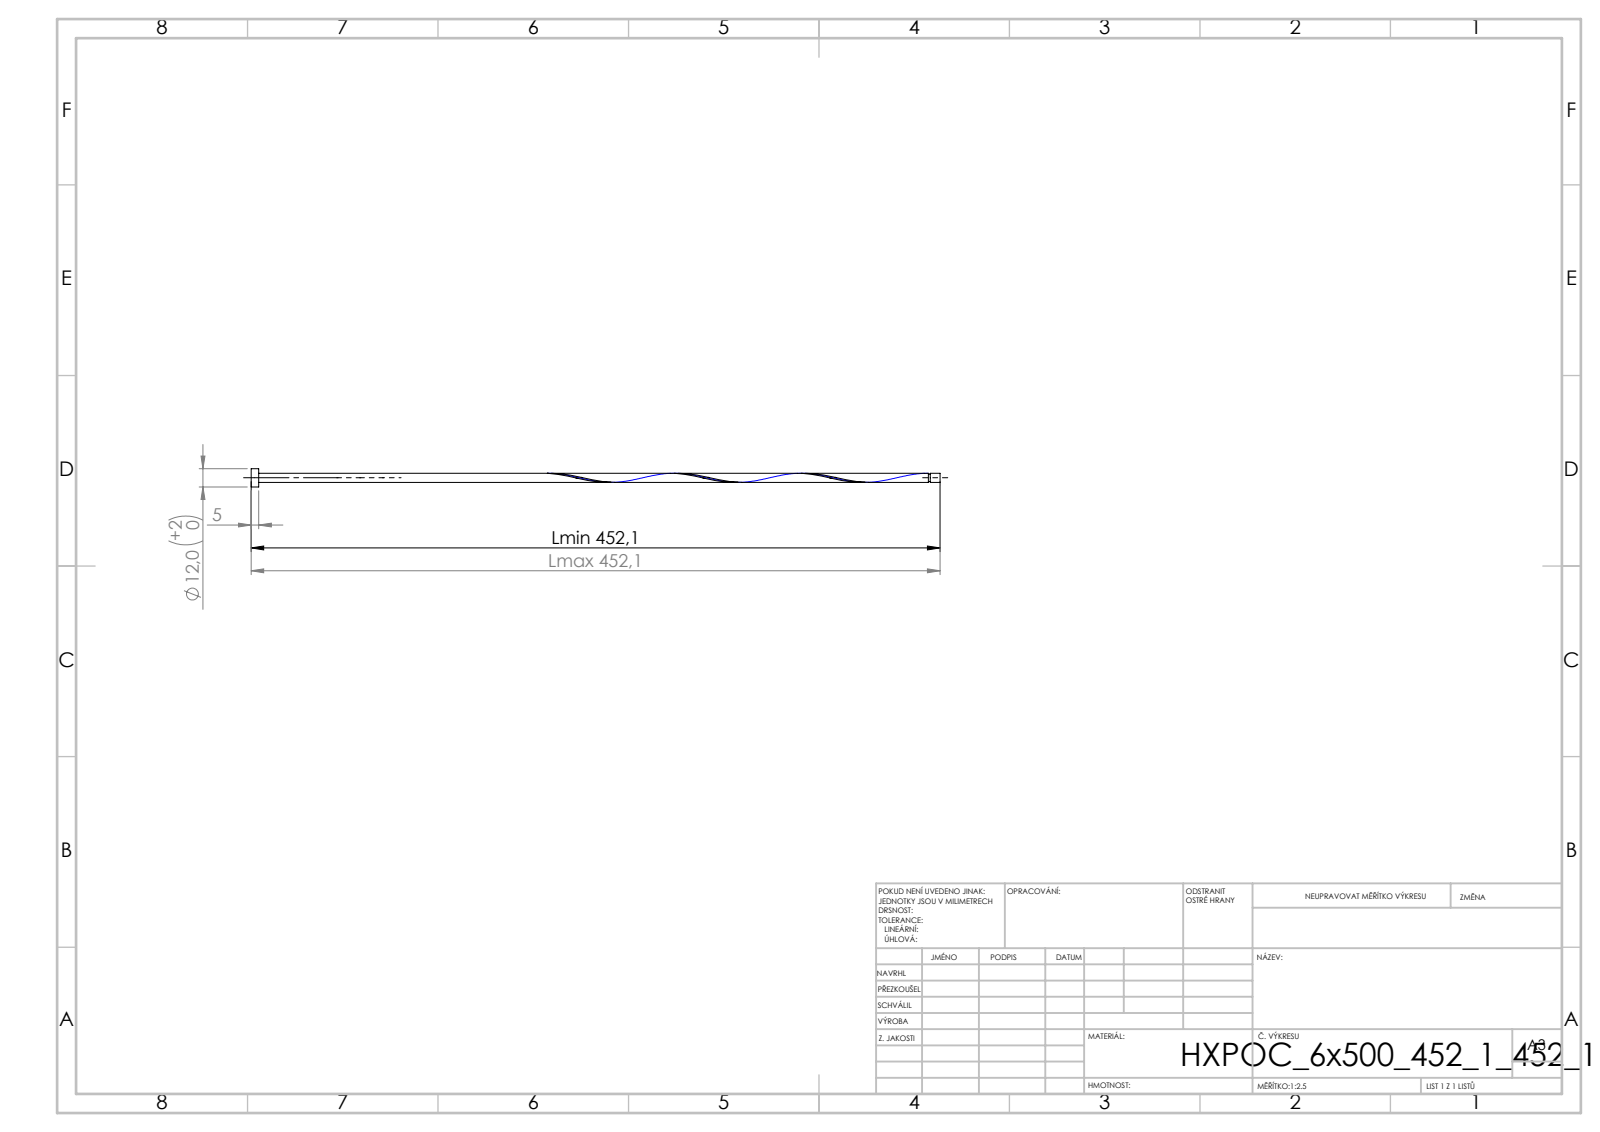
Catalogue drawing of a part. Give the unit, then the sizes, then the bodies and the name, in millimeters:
Units: millimetres
Overall size (bounding box): 452.1 × 12 × 12
Round bosses / shafts (diameter × count): ⌀12 ×1, ⌀6 ×1, ⌀4.8 ×1
Main face-to-face distances: 5, 452.1, 447.1, 445.64, 440.64, 6.46, 444.44, 439.44, 1.2, 7.66
Volume: 16 201 mm³ · Surface area: 12 145 mm²
Bodies: 1 solid, 16 faces (6 planar, 9 cylindrical, 1 other)
STEP written by: SolidWorks 2019 (CONFIG_CONTROL_DESIGN)
